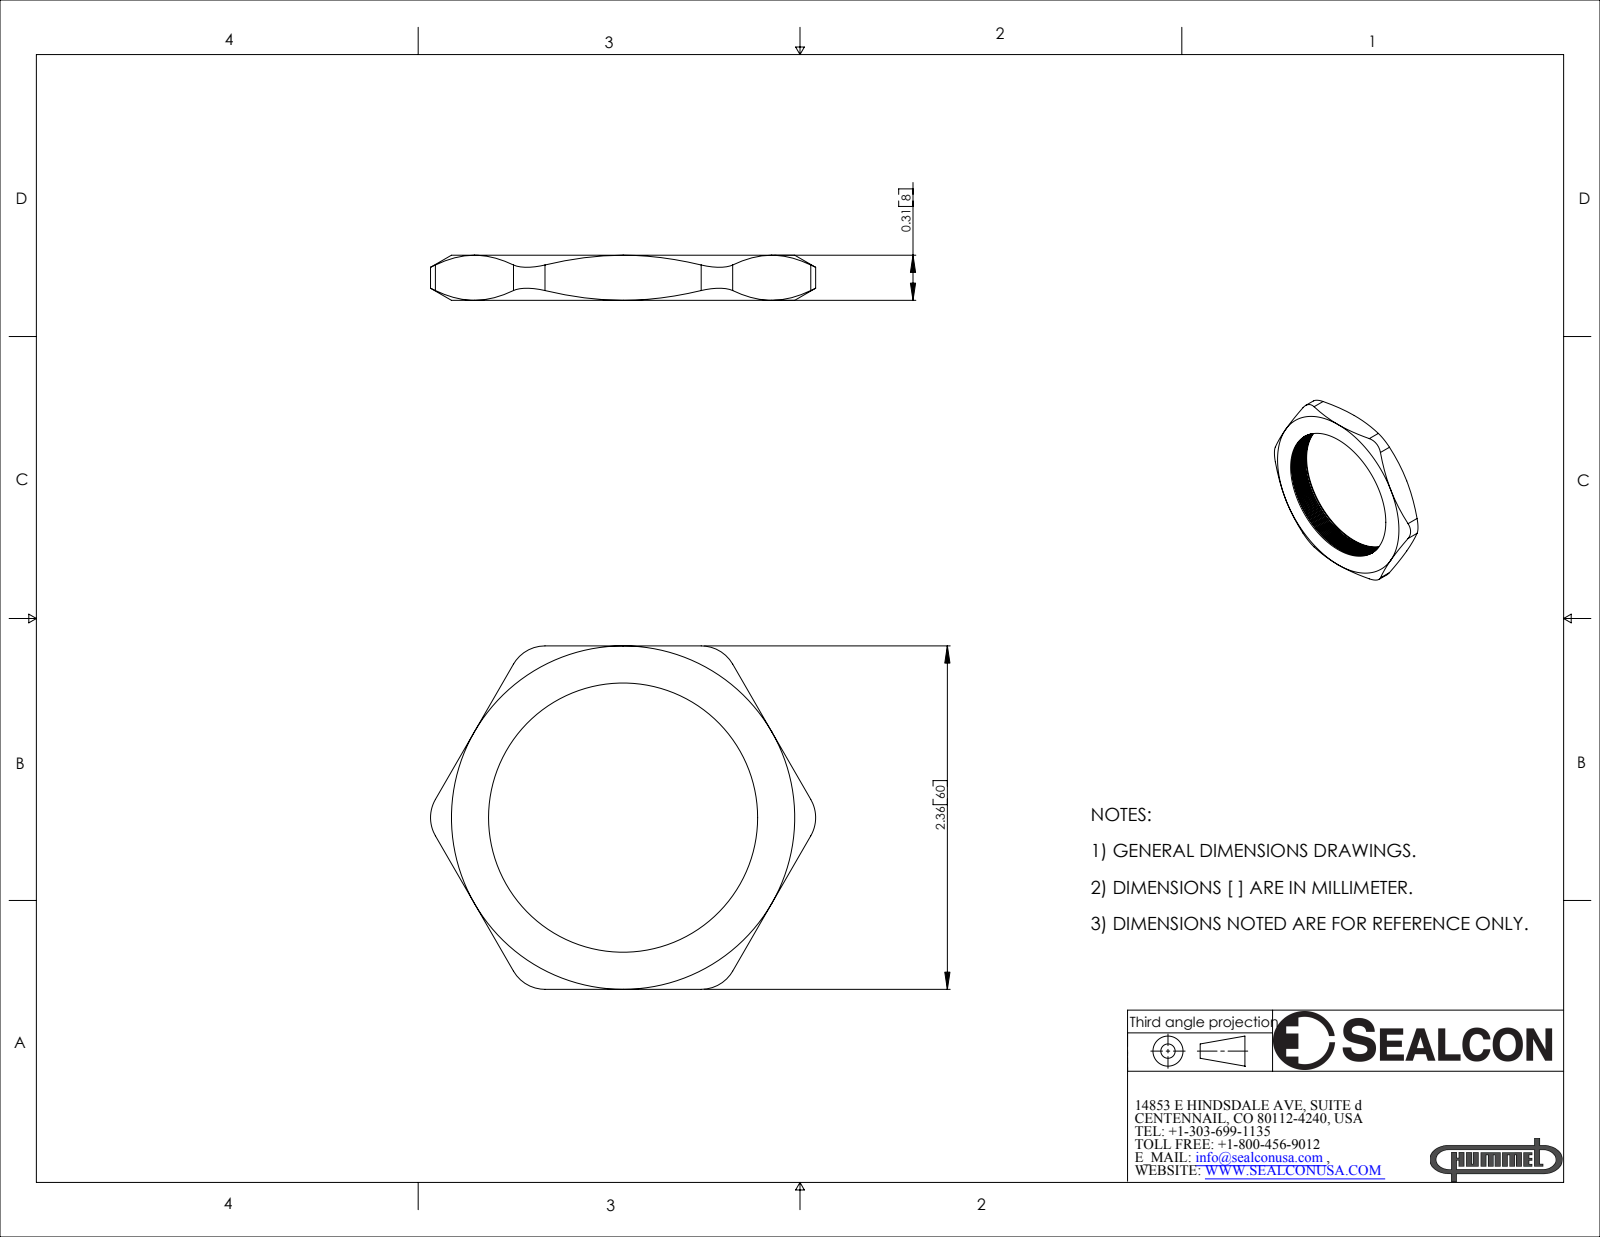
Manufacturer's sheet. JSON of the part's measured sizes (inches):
{"part_name": "NP-36", "step_written_by": "SolidWorks 2007 (CONFIG_CONTROL_DESIGN)", "units": "inches", "bodies": {"solids": 1, "faces": 101, "planar": 8, "cylindrical": 31, "other": 62}, "overall_size": [2.648, 2.36, 0.31], "volume_in3": 0.615, "surface_area_in2": 9.756, "round_holes": [[1.85, 1]], "partial_cylinders_radius": [[0.25, 6]], "face_to_face_distances": [0.31, 2.36]}
